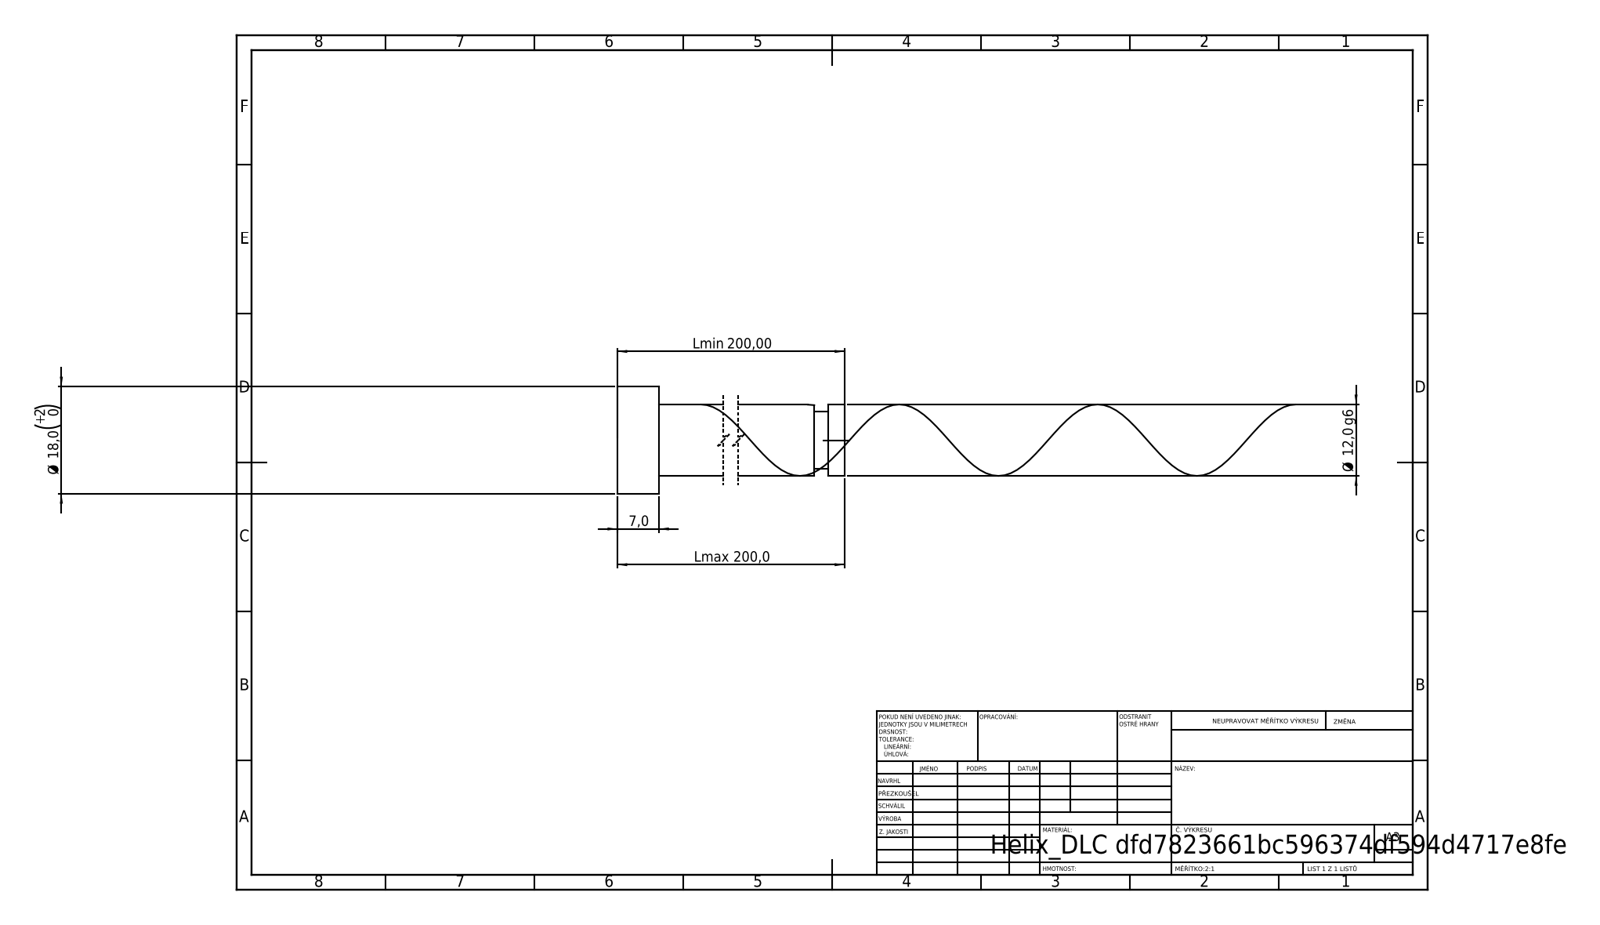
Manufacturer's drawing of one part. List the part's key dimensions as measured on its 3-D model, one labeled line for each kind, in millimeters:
STEP written by: SolidWorks 2019 (CONFIG_CONTROL_DESIGN)
Units: millimetres
Bodies: 1 solid, 21 faces (6 planar, 14 cylindrical, 1 other)
Overall size (bounding box): 200 × 18 × 18
Volume: 23 295 mm³ · Surface area: 8 445 mm²
Round bosses / shafts (diameter × count): ⌀18 ×1, ⌀12 ×1, ⌀9.6 ×1
Main face-to-face distances: 7, 200, 193, 197.33, 190.33, 2.67, 194.93, 187.93, 2.4, 5.07
